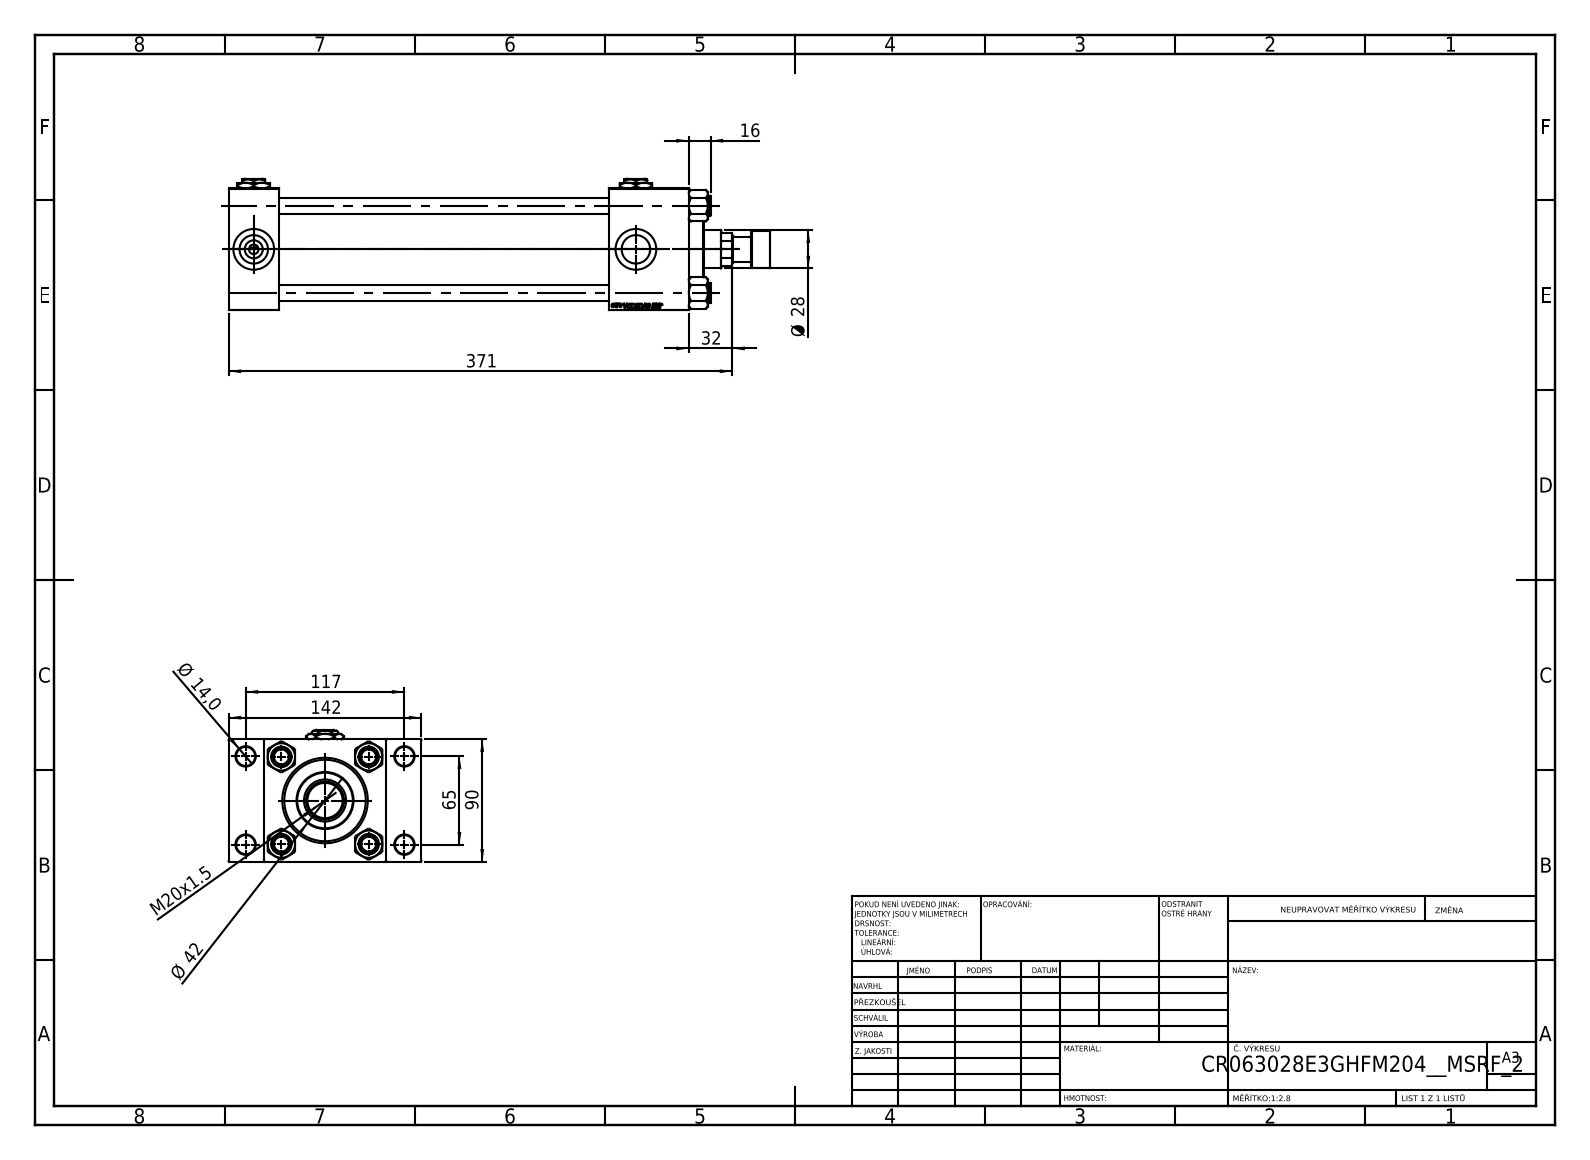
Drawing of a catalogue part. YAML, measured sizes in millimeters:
part_name: "V215CR_E_Body; V215CR_TYCINKA_E; Zatka_pro_OIL_PORT; V215_VC_A (+3 more)"
step_written_by: "SolidWorks 2019 (CONFIG_CONTROL_DESIGN)"
units: millimeters
bodies: {solids: 14, faces: 1251, planar: 550, cylindrical: 101, other: 600}
overall_size: [399, 142, 97]
volume: 1421000
surface_area: 334904
round_holes:
  - {diameter: 12, count: 4}
  - {diameter: 14, count: 4}
  - {diameter: 20.96, count: 4}
  - {diameter: 30, count: 4}
  - {diameter: 7, count: 3}
  - {diameter: 18.5, count: 1}
  - {diameter: 28, count: 1}
  - {diameter: 31, count: 1}
  - {diameter: 50, count: 1}
  - {diameter: 60, count: 1}
  - {diameter: 63, count: 1}
round_bosses_or_shafts:
  - {diameter: 15, count: 4}
  - {diameter: 69, count: 1}
  - {diameter: 42, count: 1}
  - {diameter: 27, count: 1}
  - {diameter: 18, count: 1}
face_to_face_distances: [90, 37, 339, 302, 26, 116, 59, 280, 243, 310.3]
hole_center_spacings: [26.35, 45.47, 64.3, 66.92, 69.81, 90.65, 111.34, 65]
